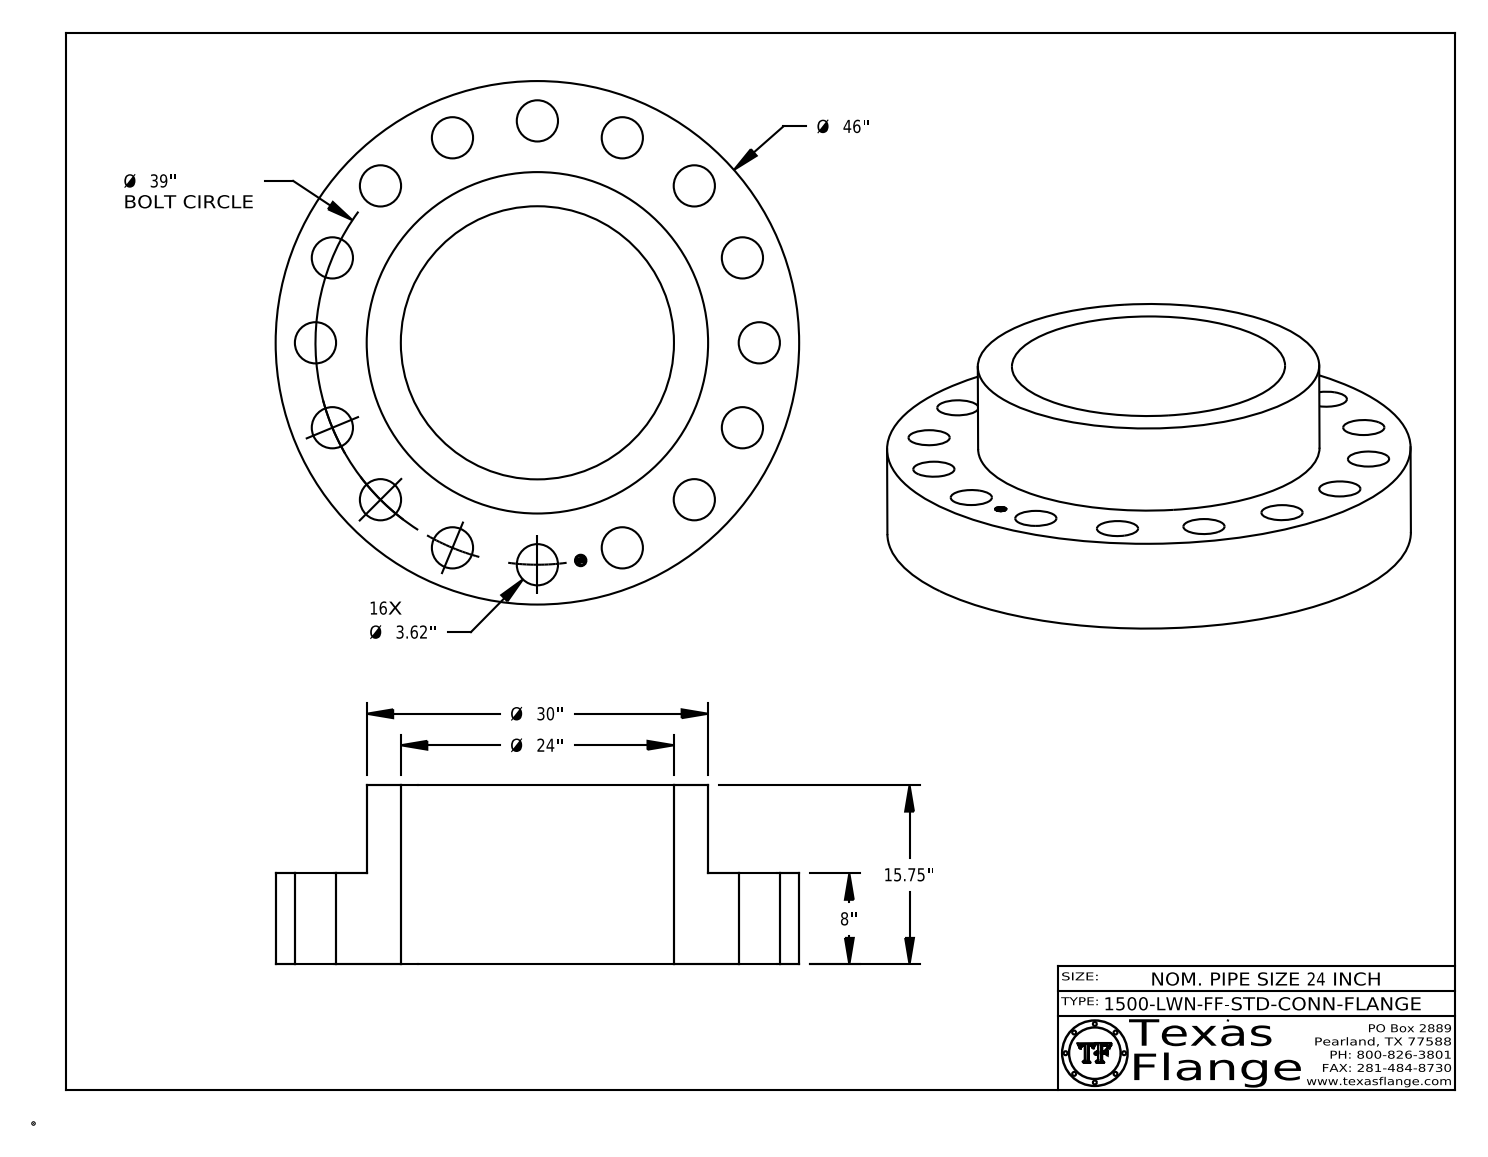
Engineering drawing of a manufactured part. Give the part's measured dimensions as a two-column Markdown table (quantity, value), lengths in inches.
| quantity | value |
| --- | --- |
| part name | 24-1500-LWN-FF-STD-CONN-FLANGE |
| STEP written by | CATIA V5 STEP AP214 (AUTOMOTIVE_DESIGN) |
| units | inches |
| bodies | 1 solid, 426 faces (368 planar, 58 cylindrical, 0 other) |
| overall size | 46 × 46 × 15.75 |
| volume | 10 331 in³ |
| surface area | 6 619 in² |
| round holes (diameter × count) | 3.62 × 16, 1 × 1, 24 × 1 |
| round bosses / shafts (diameter × count) | 0.061 × 8, 46 × 1, 30 × 1, 0.788 × 1 |
| main face-to-face distances | 8, 15.75, 7.75, 7.995, 7.755, 0.298, 0.292, 0.055, 0.193, 0.248 |
| hole center spacings | 19.5, 21.667, 27.577, 38.251, 14.925, 36.031, 7.608, 7.609 |
